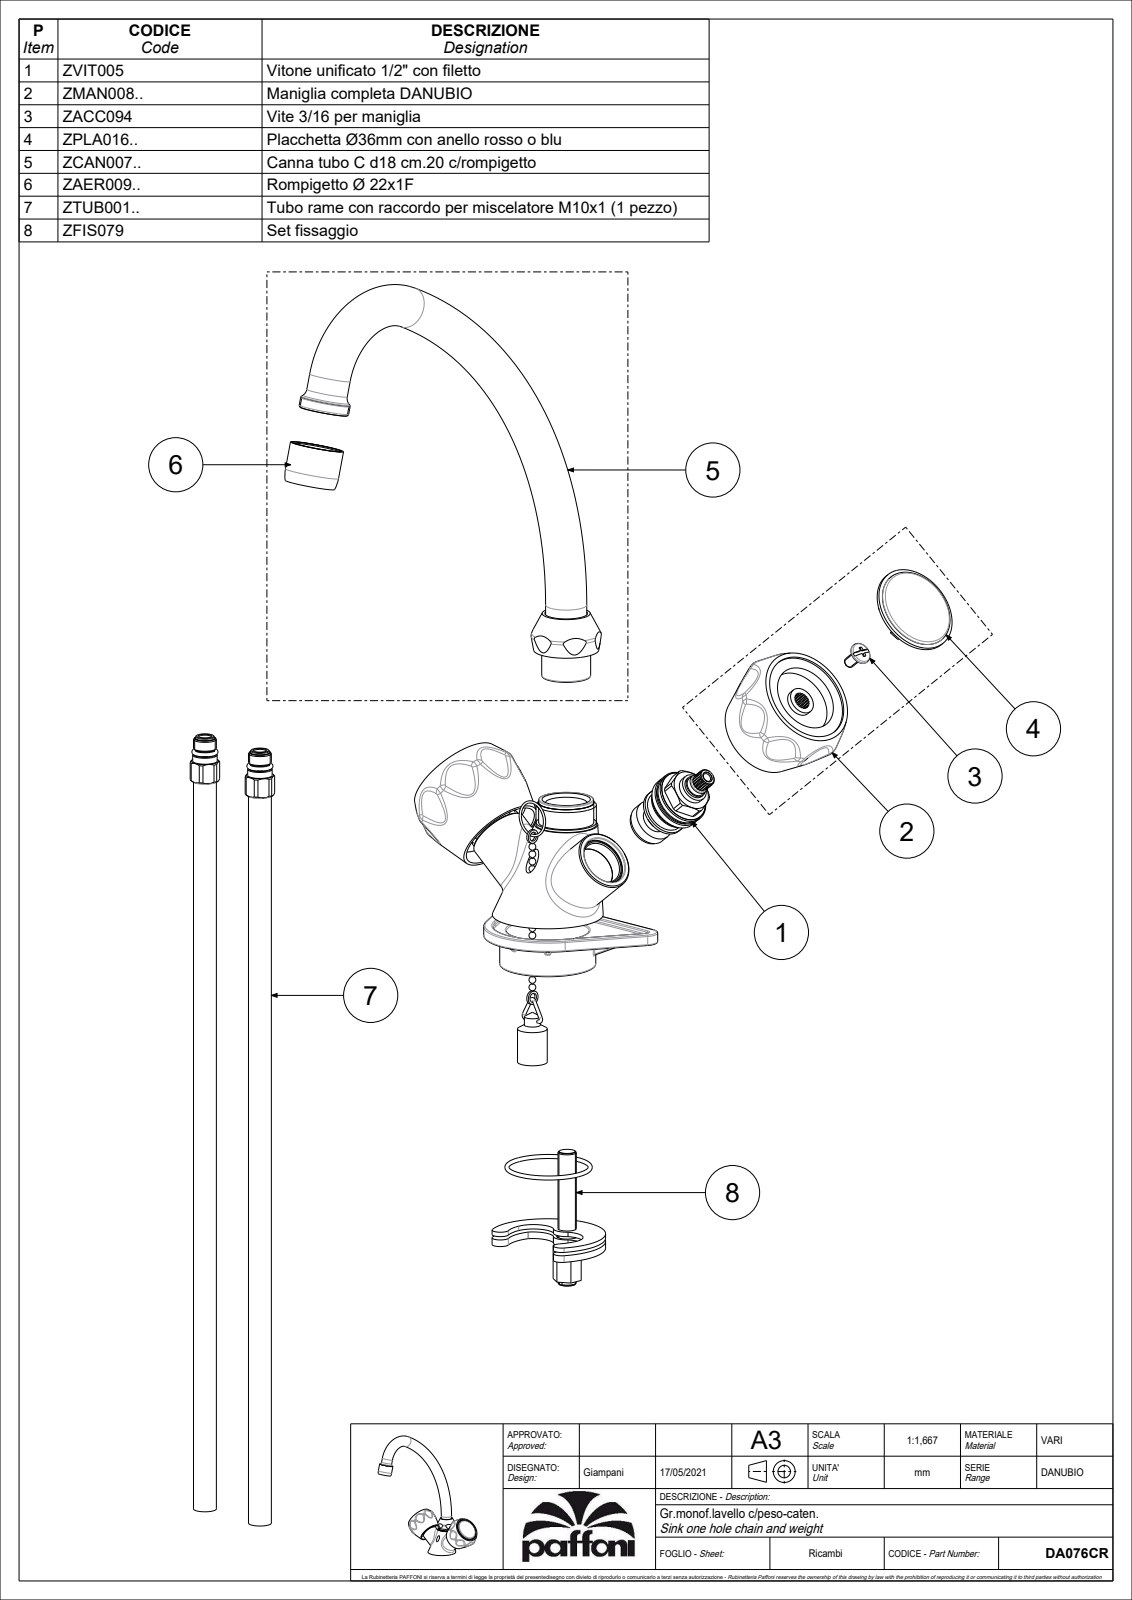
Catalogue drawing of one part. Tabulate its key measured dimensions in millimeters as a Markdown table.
| quantity | value |
| --- | --- |
| part name | DA076CR |
| STEP written by | CREO PARAMETRIC BY PTC INC, 2020044 (CONFIG_CONTROL_DESIGN) |
| units | millimeters |
| bodies | 2 solids, 457 faces (89 planar, 134 cylindrical, 234 other) |
| overall size | 228.5 × 179.45 × 145.23 |
| volume | 186 329 mm³ |
| surface area | 73 676 mm² |
| round holes (diameter × count) | 9 × 4, 21 × 3, 11 × 2, 16.4 × 2, 18 × 2, 19 × 2, 21.5 × 2, 4 × 1, 6 × 1, 12 × 1, 14.6 × 1, 16 × 1 |
| round bosses / shafts (diameter × count) | 38.5 × 2, 26.3 × 2, 18 × 2, 26.4 × 1, 24 × 1, 23.6 × 1, 20.8 × 1, 19.8 × 1 |
| partial cylindrical surfaces (radius × count) | 21.31 × 16, 2.5 × 1 |
| main face-to-face distances | 35.31, 0.4, 35.71, 0.6, 56.01, 55.61, 20.3, 1, 0.8, 4.2 |
| hole center spacings | 13.38, 14 |
